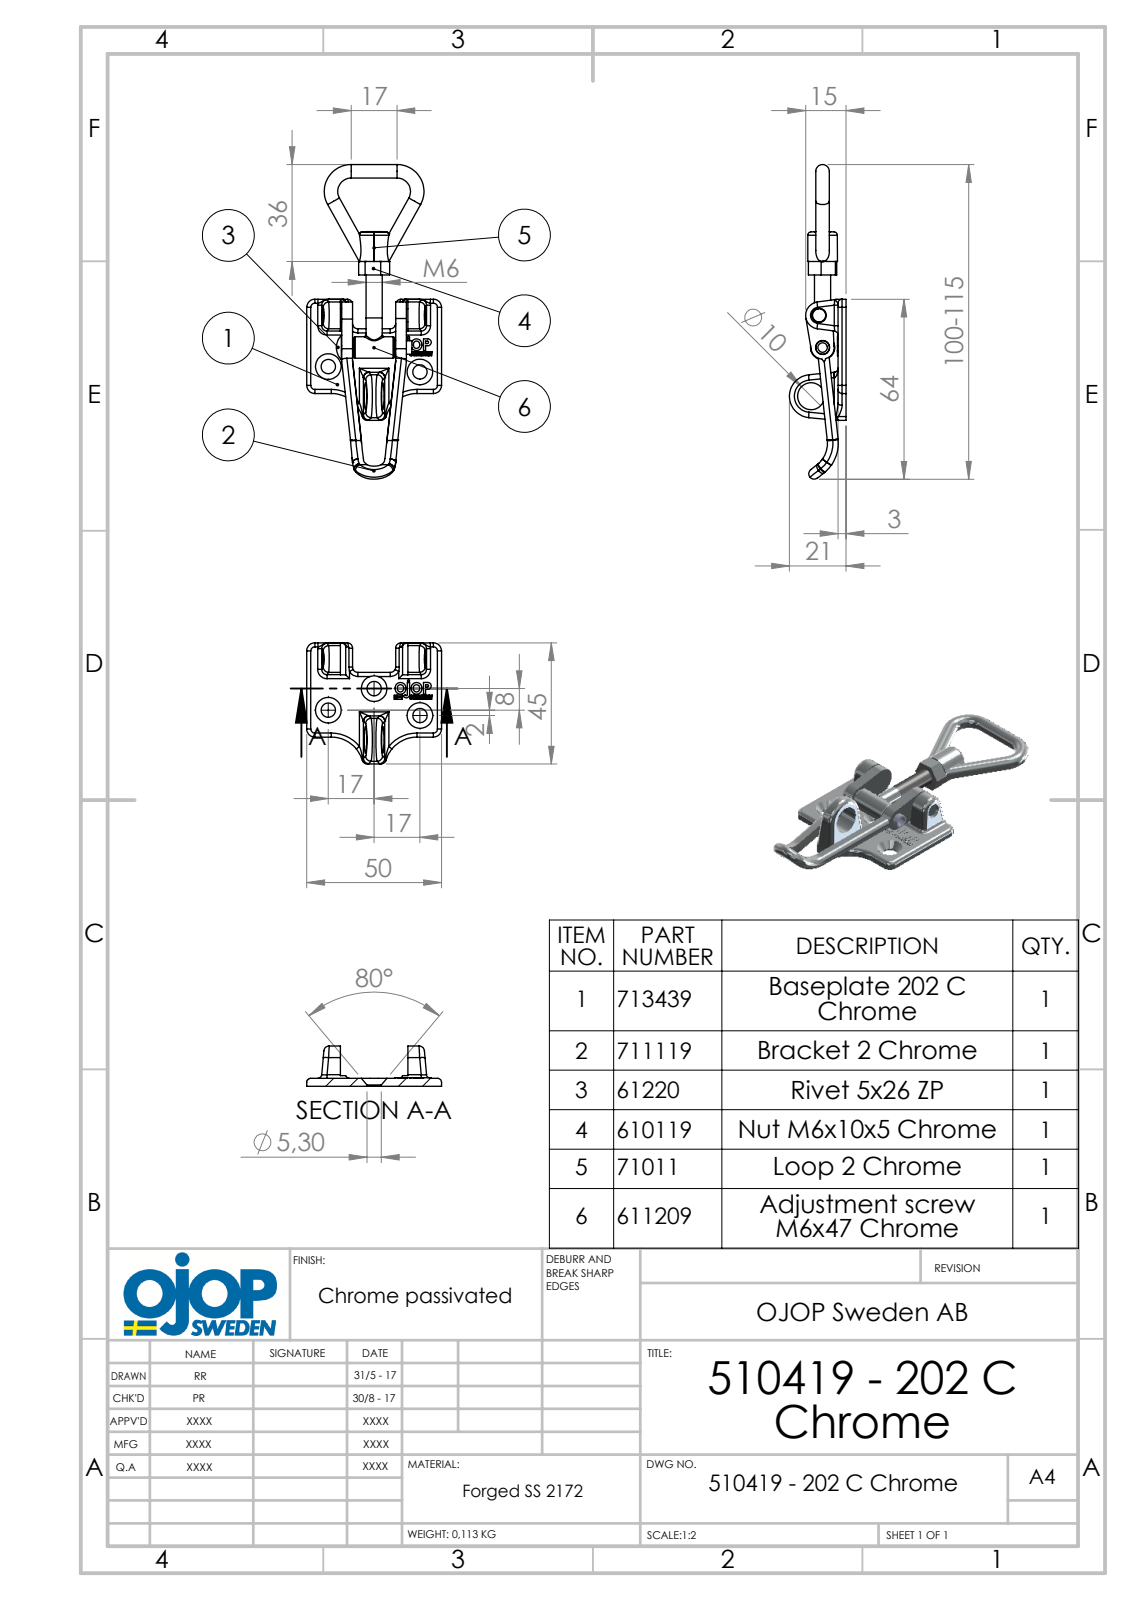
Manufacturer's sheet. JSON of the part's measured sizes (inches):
{"part_name": "Justerskruv M6; 202 C; Ring 2; 510419 - 202 C Kromad (+3 more)", "step_written_by": "SolidWorks 2015 (AUTOMOTIVE_DESIGN)", "units": "inches", "bodies": {"solids": 6, "faces": 263, "planar": 70, "cylindrical": 99, "other": 94}, "overall_size": [4.778, 1.969, 0.827], "volume_in3": 0.943, "surface_area_in2": 19.3, "round_holes": [[0.24, 2], [0.079, 1], [0.205, 1], [0.209, 1], [0.394, 1]], "round_bosses_or_shafts": [[0.197, 4], [0.354, 1], [0.315, 1], [0.237, 1], [0.236, 1], [0.191, 1]], "partial_cylinders_radius": [[0.079, 21], [0.059, 7], [0.118, 4], [0.216, 4], [0.049, 2], [0.197, 2], [0.315, 2], [0.157, 1]], "face_to_face_distances": [0.118, 0.157, 0.787, 0.63, 0.02, 0.177, 0.945, 0.807, 0.965, 0.394], "hole_center_spacings": [0.472, 0.721, 1.18]}
